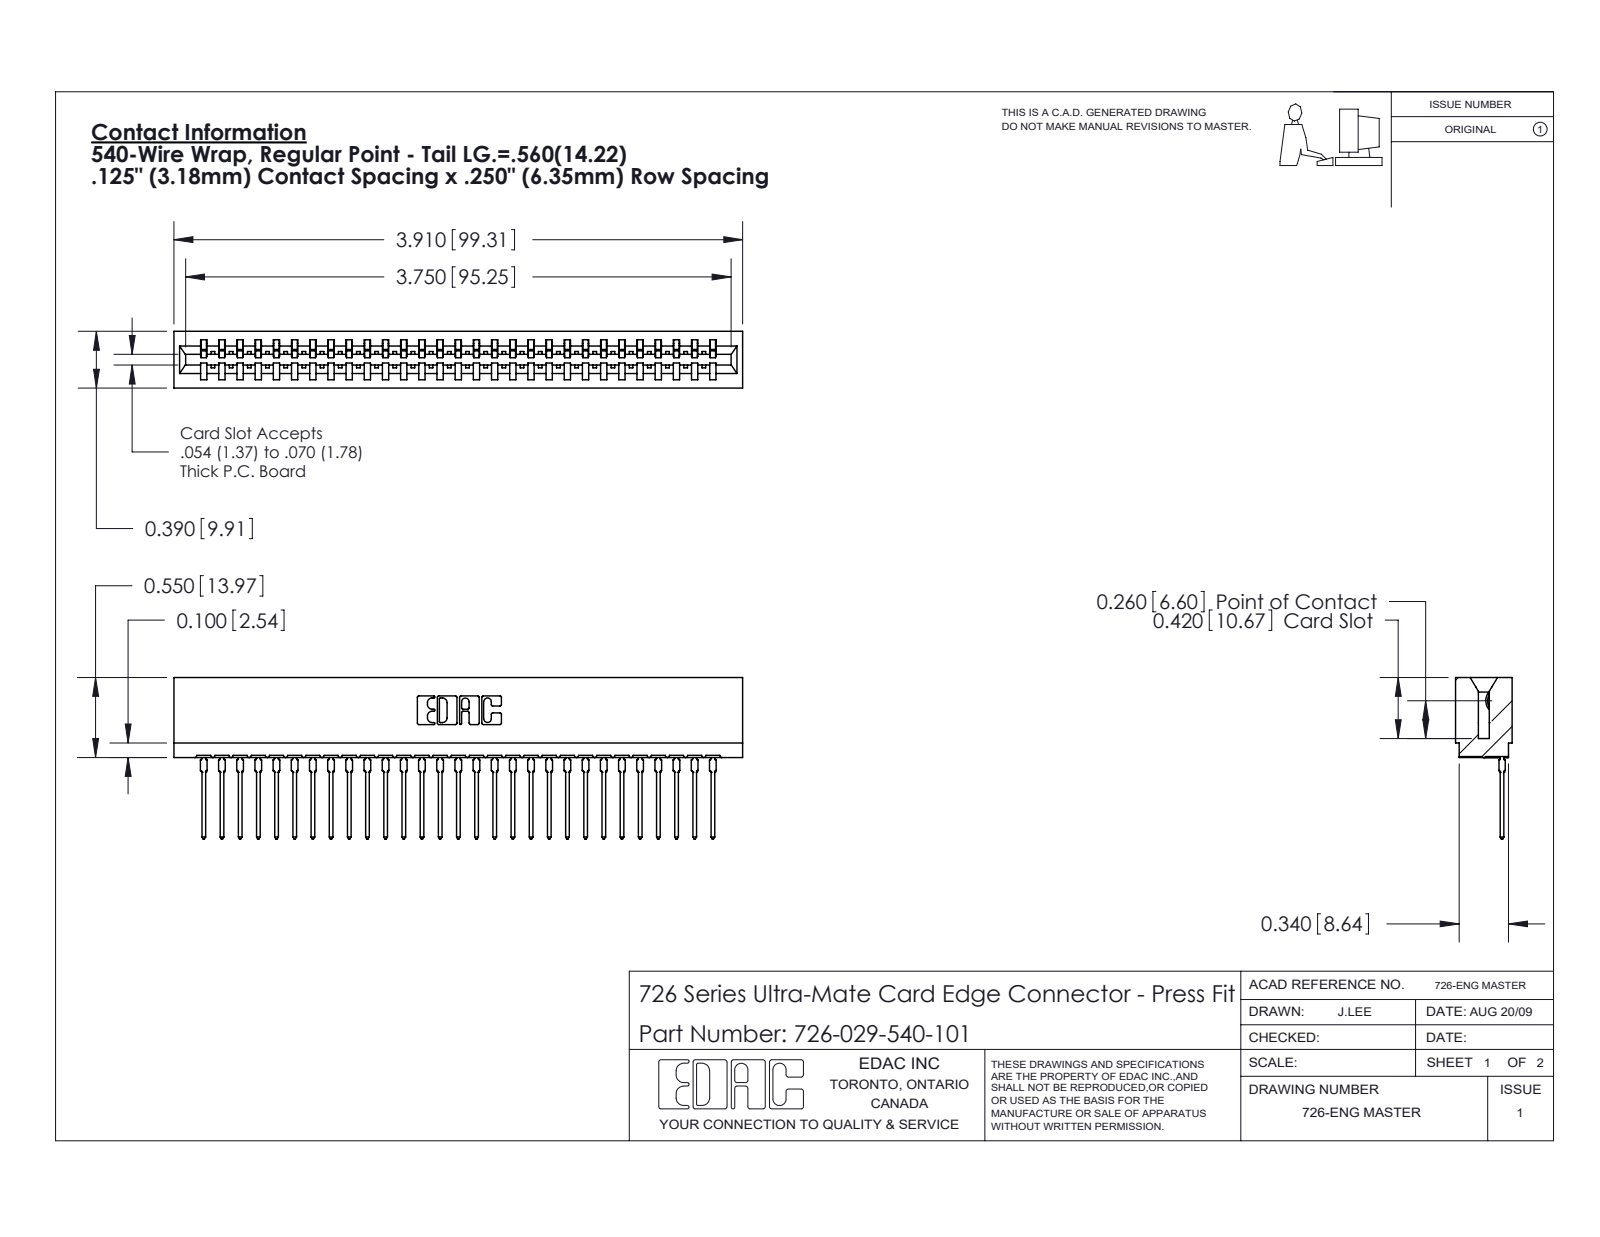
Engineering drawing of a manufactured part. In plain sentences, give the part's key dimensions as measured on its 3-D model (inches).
The part is named "726 Part_.515 Slot Depth - 01; 726-029-540-101; 746-292-001_540". Its 3-D file was written by "SolidWorks 2020 (CONFIG_CONTROL_DESIGN)". It is 30 solids with 3229 faces: 1882 planar, 593 cylindrical and 754 other. Overall it measures 3.91 by 1.109 by 0.39 inches. Its volume is 0.55 cubic inches and its surface area 21.56 square inches. Partial cylindrical surfaces (rounded edges, fillets, slot ends): 58 of radius 0.021, 30 of radius 0.015, 22 of radius 0.01, 6 of radius 0.007, 6 of radius 0.031, 4 of radius 0.005, 4 of radius 0.011, 3 of radius 0.026. The main face-to-face distances are 0.057, 0.333, 0.39, 0.025, 0.307, 0.25, 0.5, 0.083, 0.275, 0.75.
